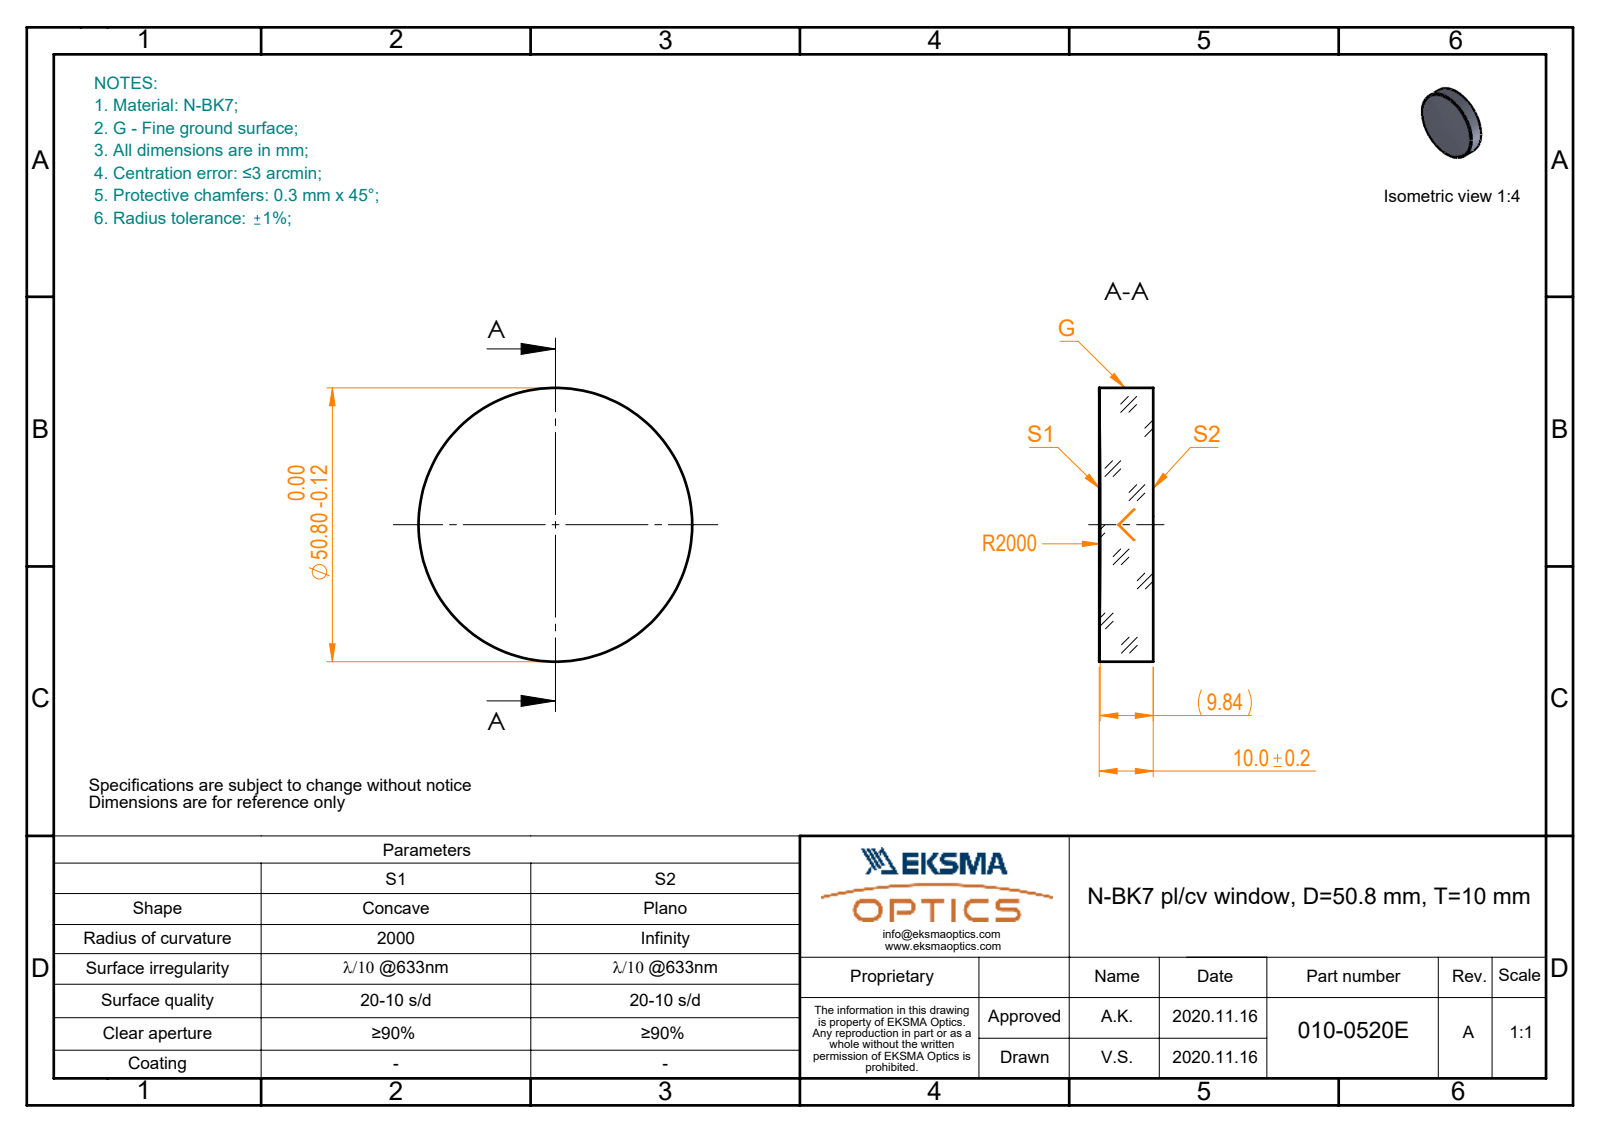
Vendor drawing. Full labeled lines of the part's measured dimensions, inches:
Part name (STEP PRODUCT): 010-0520E_N-BK7_PCV_window
STEP written by: SolidWorks 2019 (CONFIG_CONTROL_DESIGN)
Units: inches
Bodies: 1 solid, 5 faces (1 planar, 2 cylindrical, 2 other)
Overall size (bounding box): 2 × 2 × 0.394
Volume: 1.227 in³ · Surface area: 8.758 in²
Round bosses / shafts (diameter × count): ⌀2 ×1
